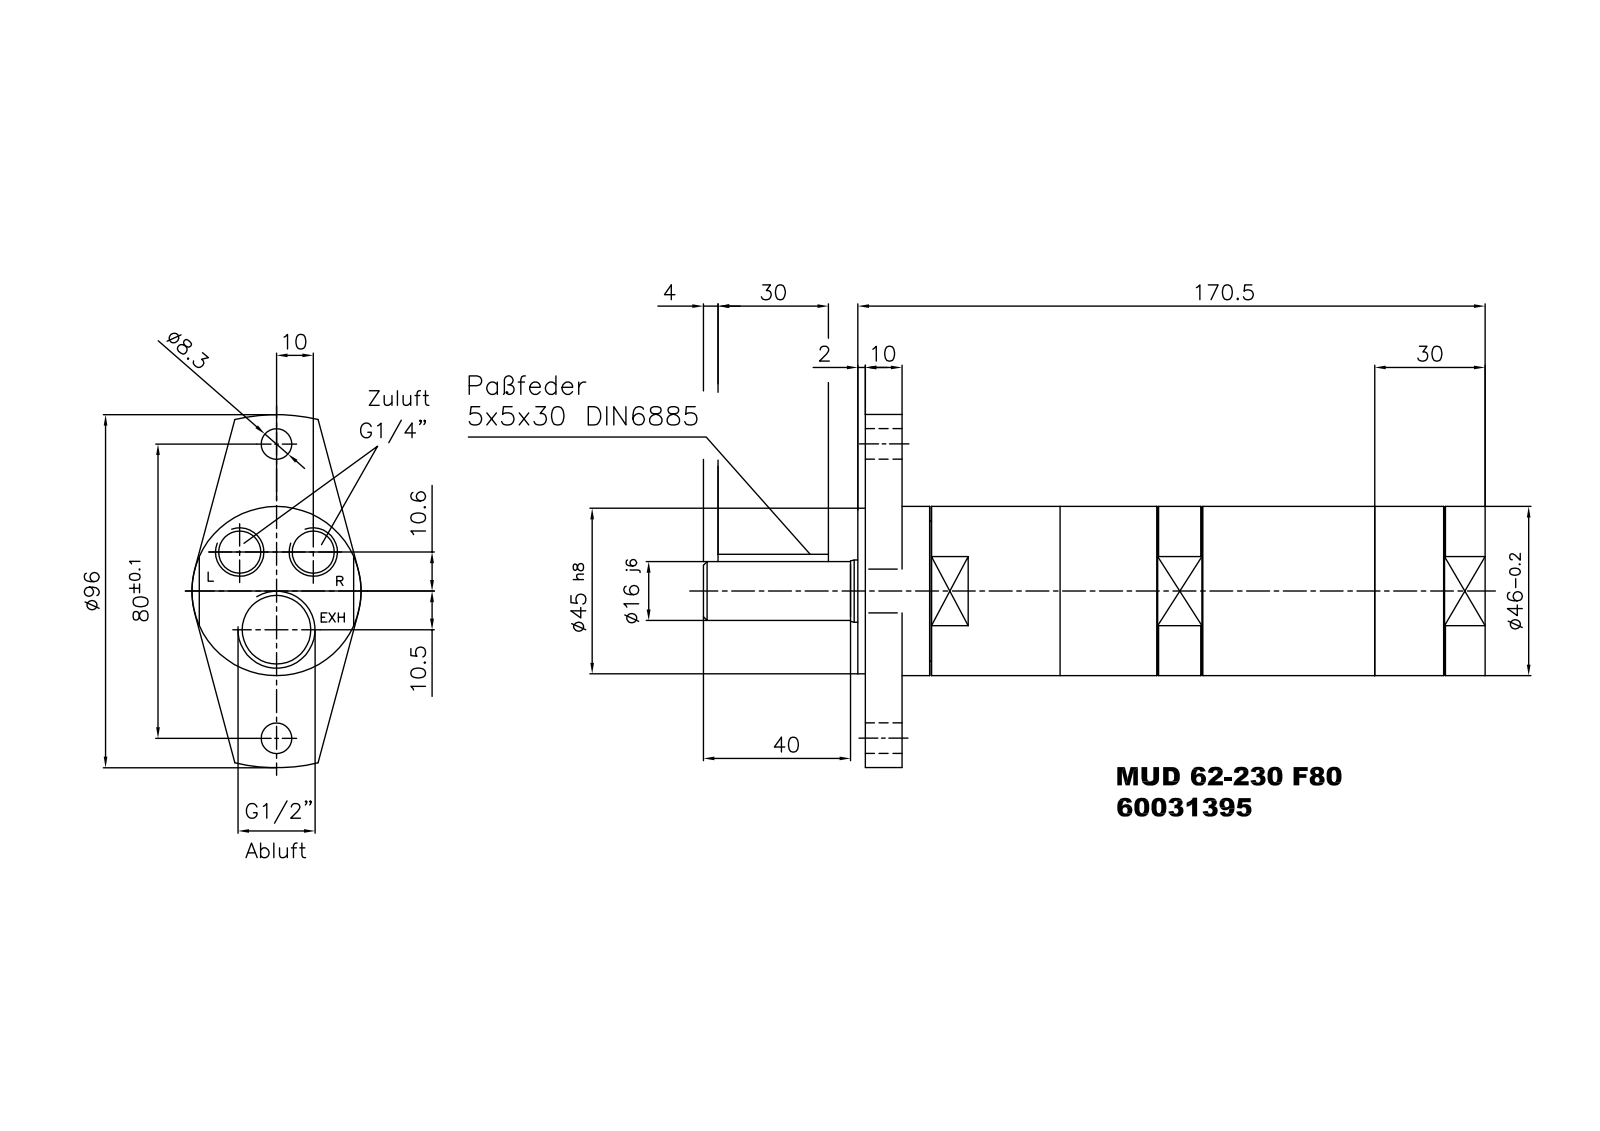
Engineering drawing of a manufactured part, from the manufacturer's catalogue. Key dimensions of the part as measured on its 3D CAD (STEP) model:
Part name (STEP PRODUCT): MUD 62-525 370 230 F80 212,5mm
STEP written by: Autodesk Inventor 2013 (AUTOMOTIVE_DESIGN)
Units: millimetres
Bodies: 1 solid, 186 faces (119 planar, 24 cylindrical, 43 other)
Overall size (bounding box): 212.5 × 96 × 46
Volume: 299 042 mm³ · Surface area: 38 554 mm²
Round holes (diameter × count): ⌀8.3 ×2, ⌀11.45 ×2, ⌀1.6 ×1, ⌀17.5 ×1, ⌀18.63 ×1
Round bosses / shafts (diameter × count): ⌀46 ×1, ⌀45 ×1, ⌀40 ×1, ⌀16.95 ×1, ⌀16 ×1
Partial cylindrical surfaces — rounded edges, fillets, slot ends (radius × count): R2.5 ×2, R48 ×1
Main face-to-face distances: 10, 12, 2, 158.5, 170.5, 168.5, 138.5, 30, 140.5, 17.5
Hole centre spacings: 14.57, 23.35, 31.05, 40, 51.58, 10.5, 20, 29.5
